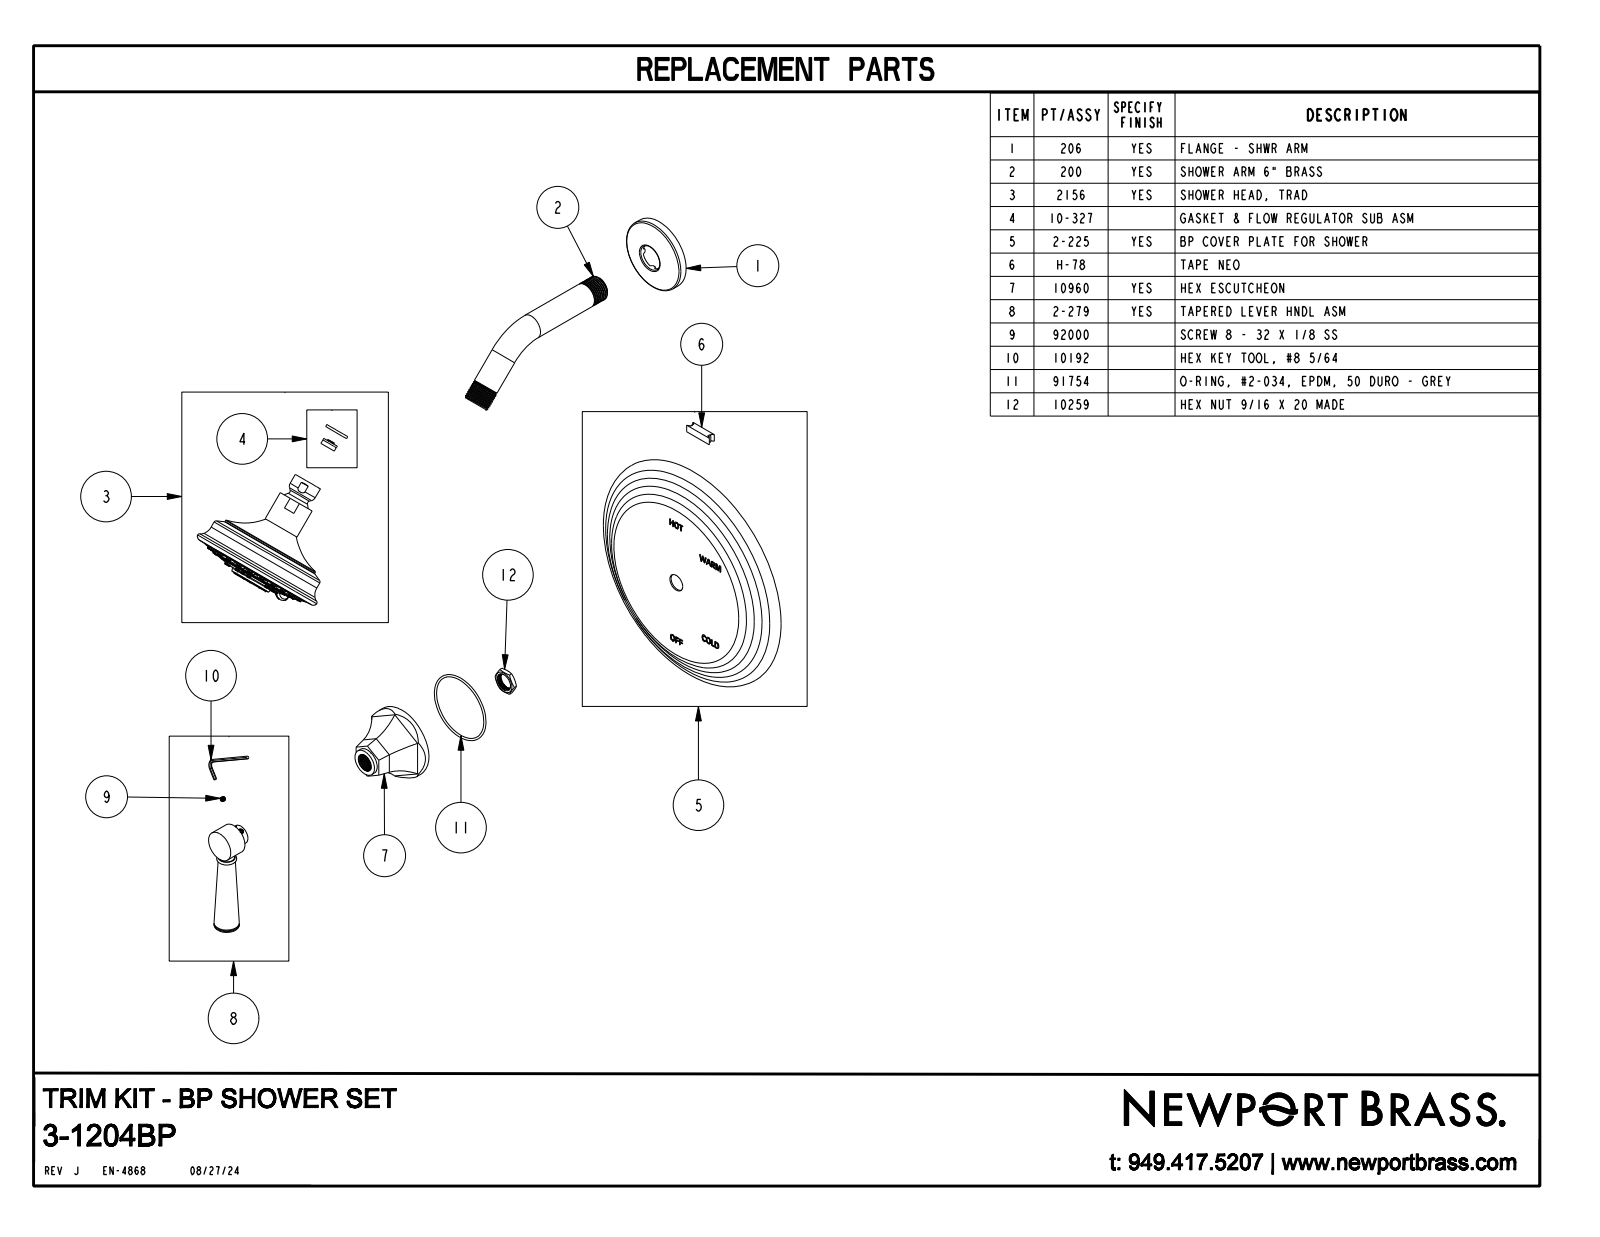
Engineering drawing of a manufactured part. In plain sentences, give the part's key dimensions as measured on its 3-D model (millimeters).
The part is named "3-1204BP". Its 3-D file was written by "CREO PARAMETRIC BY PTC INC, 2018400 (CONFIG_CONTROL_DESIGN)". It is 2 solids with 1320 faces: 271 planar, 212 cylindrical and 837 other. Overall it measures 458.9 by 209.6 by 196.9 millimeters. Its volume is 860 800 cubic millimeters and its surface area 124 300 square millimeters. Round holes: 8 of diameter 1.5, 1 of diameter 9.8, 1 of diameter 23.5. Round bosses or shafts: 39 of diameter 3.6, 23 of diameter 4.2, 2 of diameter 20.7, 1 of diameter 96.8, 1 of diameter 94.6, 1 of diameter 82.3, 1 of diameter 60.5, 1 of diameter 60.3. Partial cylindrical surfaces (rounded edges, fillets, slot ends): 8 of radius 2, 6 of radius 39.1, 2 of radius 0.5, 1 of radius 3.5, 1 of radius 12, 1 of radius 13, 1 of radius 16. The main face-to-face distances are 19.2, 1.6, 3, 4.6, 68.9, 49.7, 73.2, 70.2, 68.6, 57.9. The hole center spacings are 14.7, 11.3, 27.2, 20.8, 20.8, 29.4, 11.3, 27.2.
